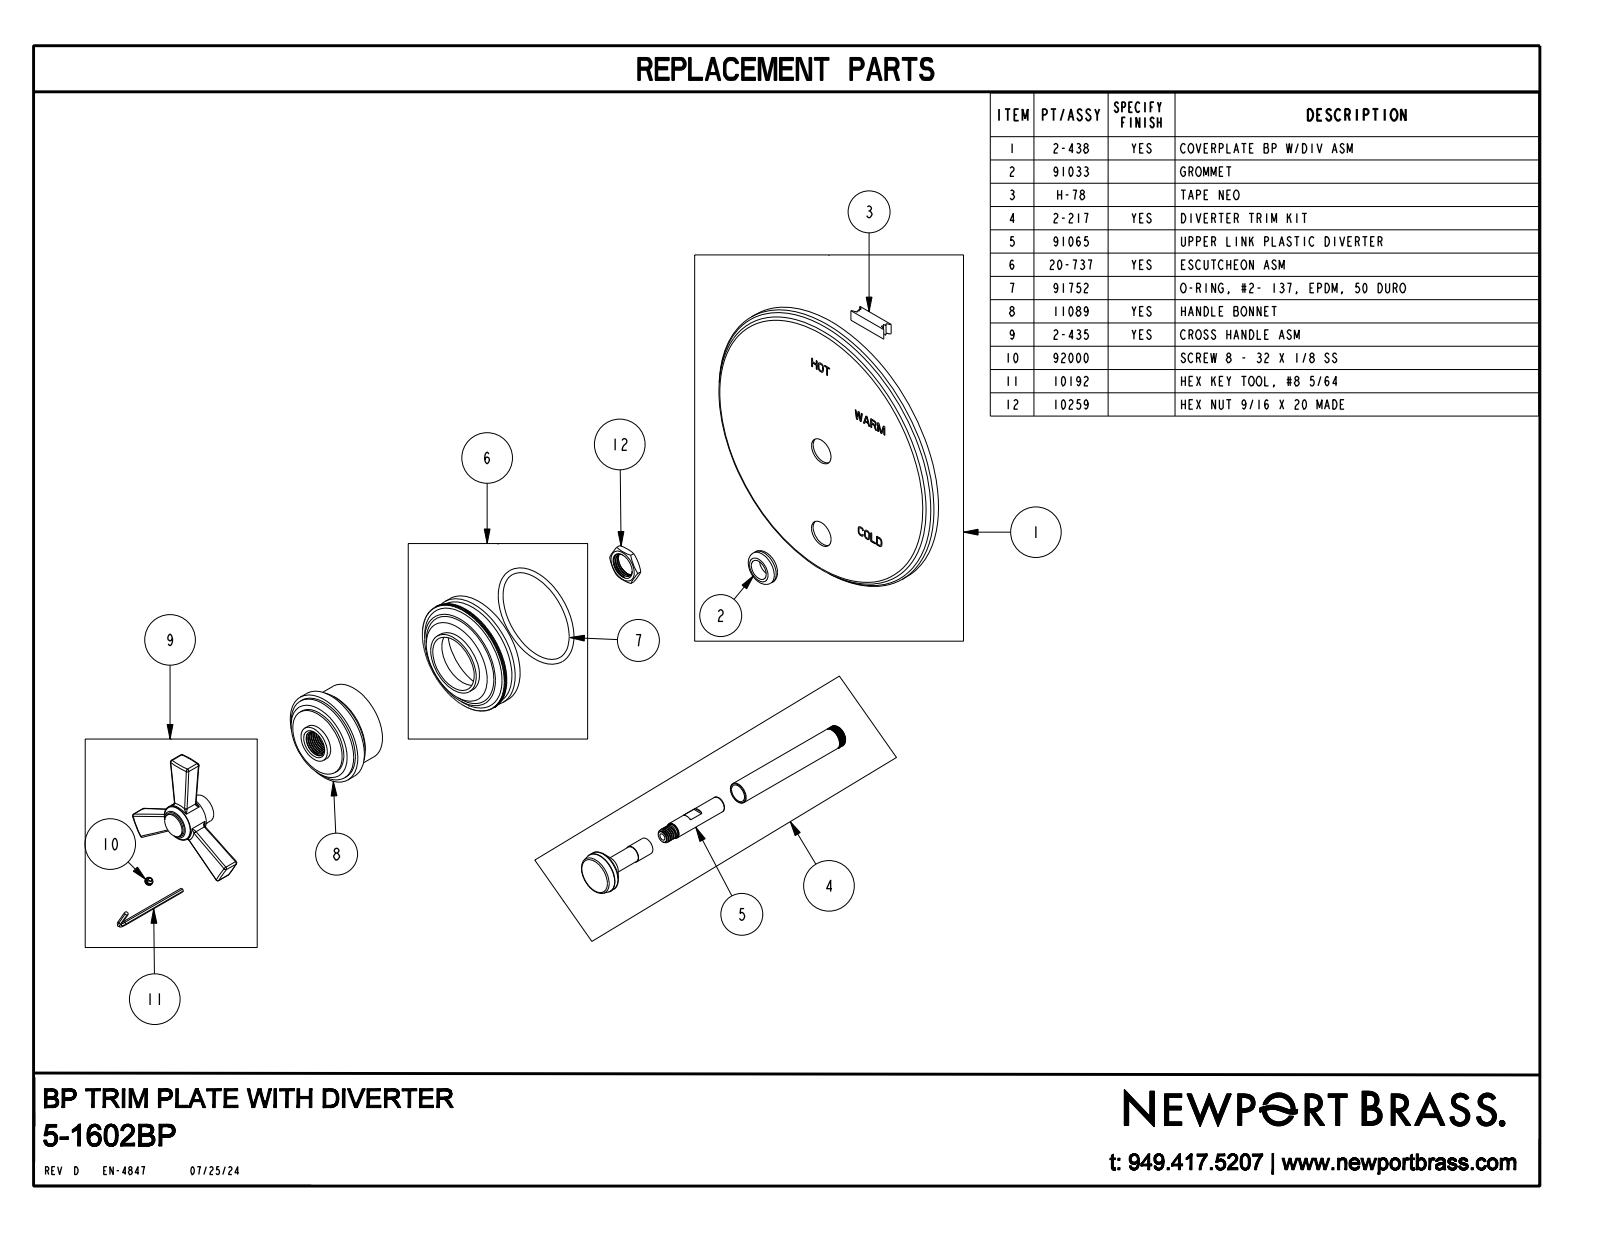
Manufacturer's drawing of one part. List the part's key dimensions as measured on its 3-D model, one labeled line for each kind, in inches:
Part name (STEP PRODUCT): 5-1602BP
STEP written by: CREO PARAMETRIC BY PTC INC, 2018400 (CONFIG_CONTROL_DESIGN)
Units: inches
Bodies: 1 solid, 982 faces (648 planar, 224 cylindrical, 110 other)
Overall size (bounding box): 6.5 × 6.5 × 3.131
Volume: 17.3 in³ · Surface area: 95.16 in²
Round bosses / shafts (diameter × count): ⌀6.5 ×1, ⌀2.5 ×1, ⌀2.4 ×1, ⌀2.05 ×1, ⌀1.9 ×1, ⌀1.75 ×1, ⌀1.5 ×1, ⌀0.9 ×1
Partial cylindrical surfaces — rounded edges, fillets, slot ends (radius × count): R0.04 ×6, R0.1 ×6
Main face-to-face distances: 0.313, 2.088, 1.775, 0.2, 0.1, 1.3, 0.15, 0.4, 1.375, 0.9
